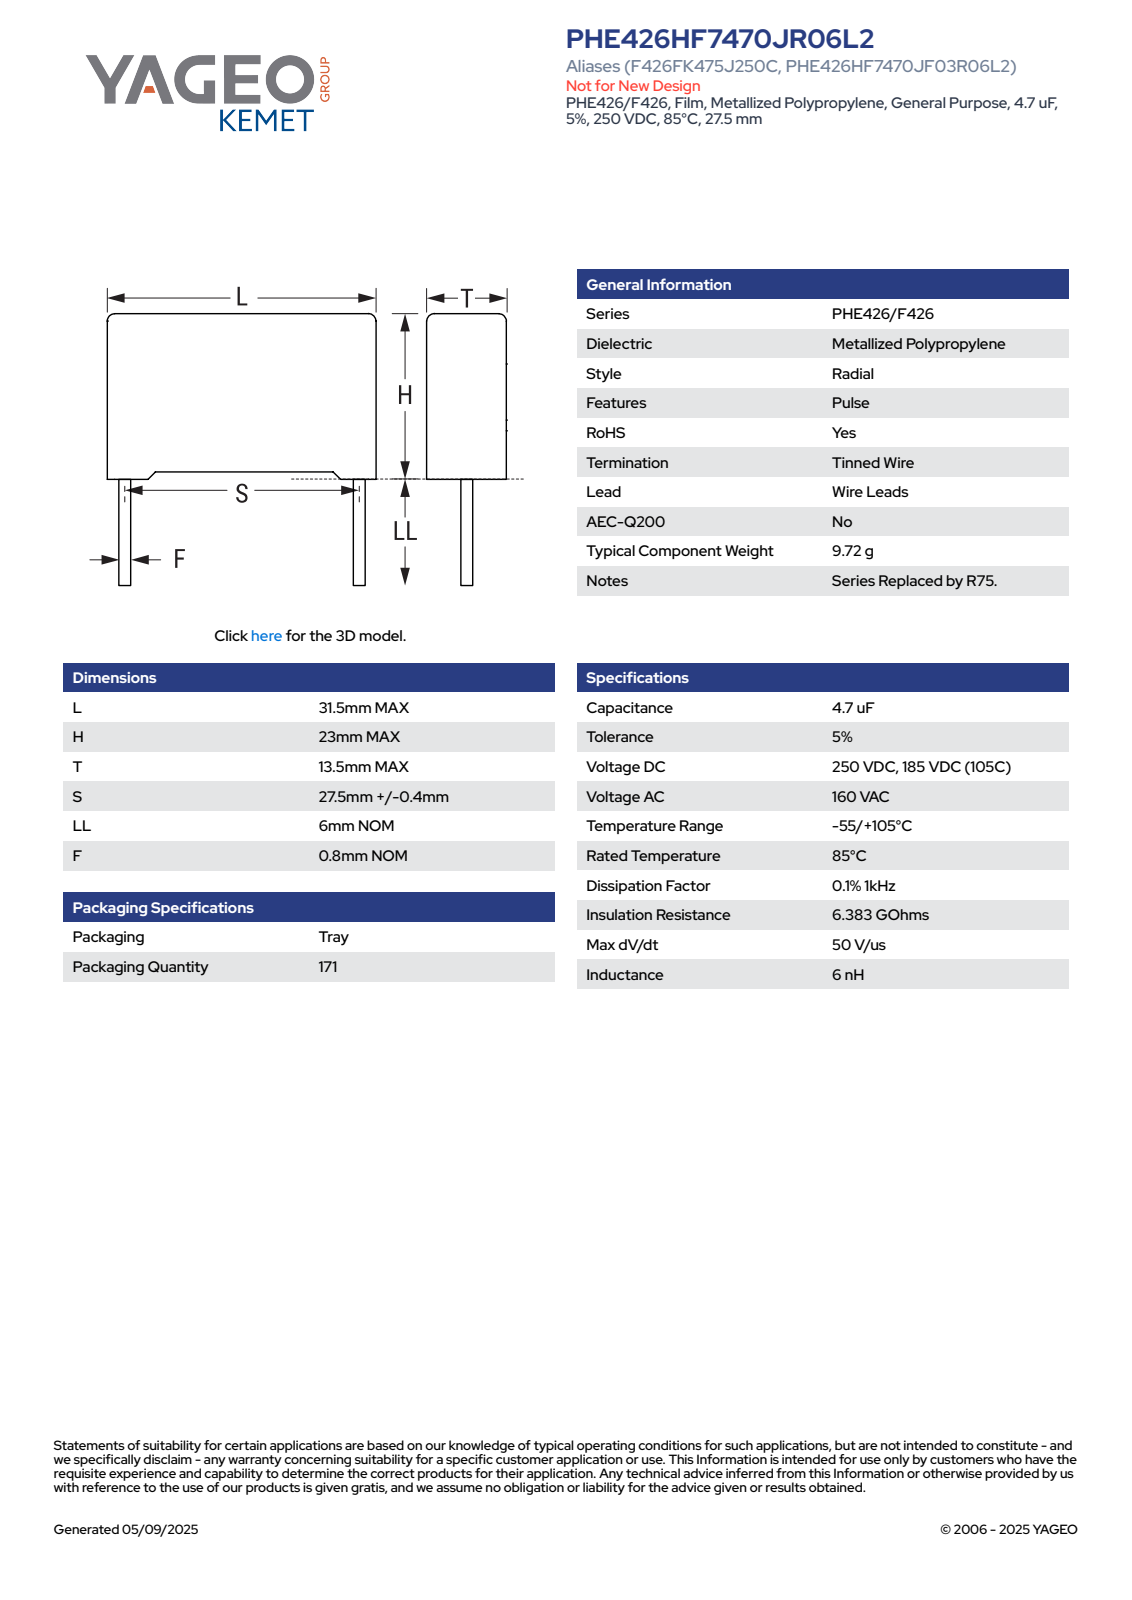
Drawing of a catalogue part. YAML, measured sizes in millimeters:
part_name: "CFR_RB2_31.5X23X13.5_L31.5H23T13.5S27.5LL6F0.8"
step_written_by: "SolidWorks 2021 (AUTOMOTIVE_DESIGN)"
units: millimeters
bodies: {solids: 4, faces: 85, planar: 77, cylindrical: 8, other: 0}
overall_size: [31.5, 29, 13.51]
volume: 9481
surface_area: 2999
round_bosses_or_shafts:
  - {diameter: 0.8, count: 2}
partial_cylinders:
  - {radius: 0.5, count: 4}
face_to_face_distances: [13.5, 22.21, 31.5, 22.25, 0.75, 0.79, 23, 1.05, 30.45, 12.45]
